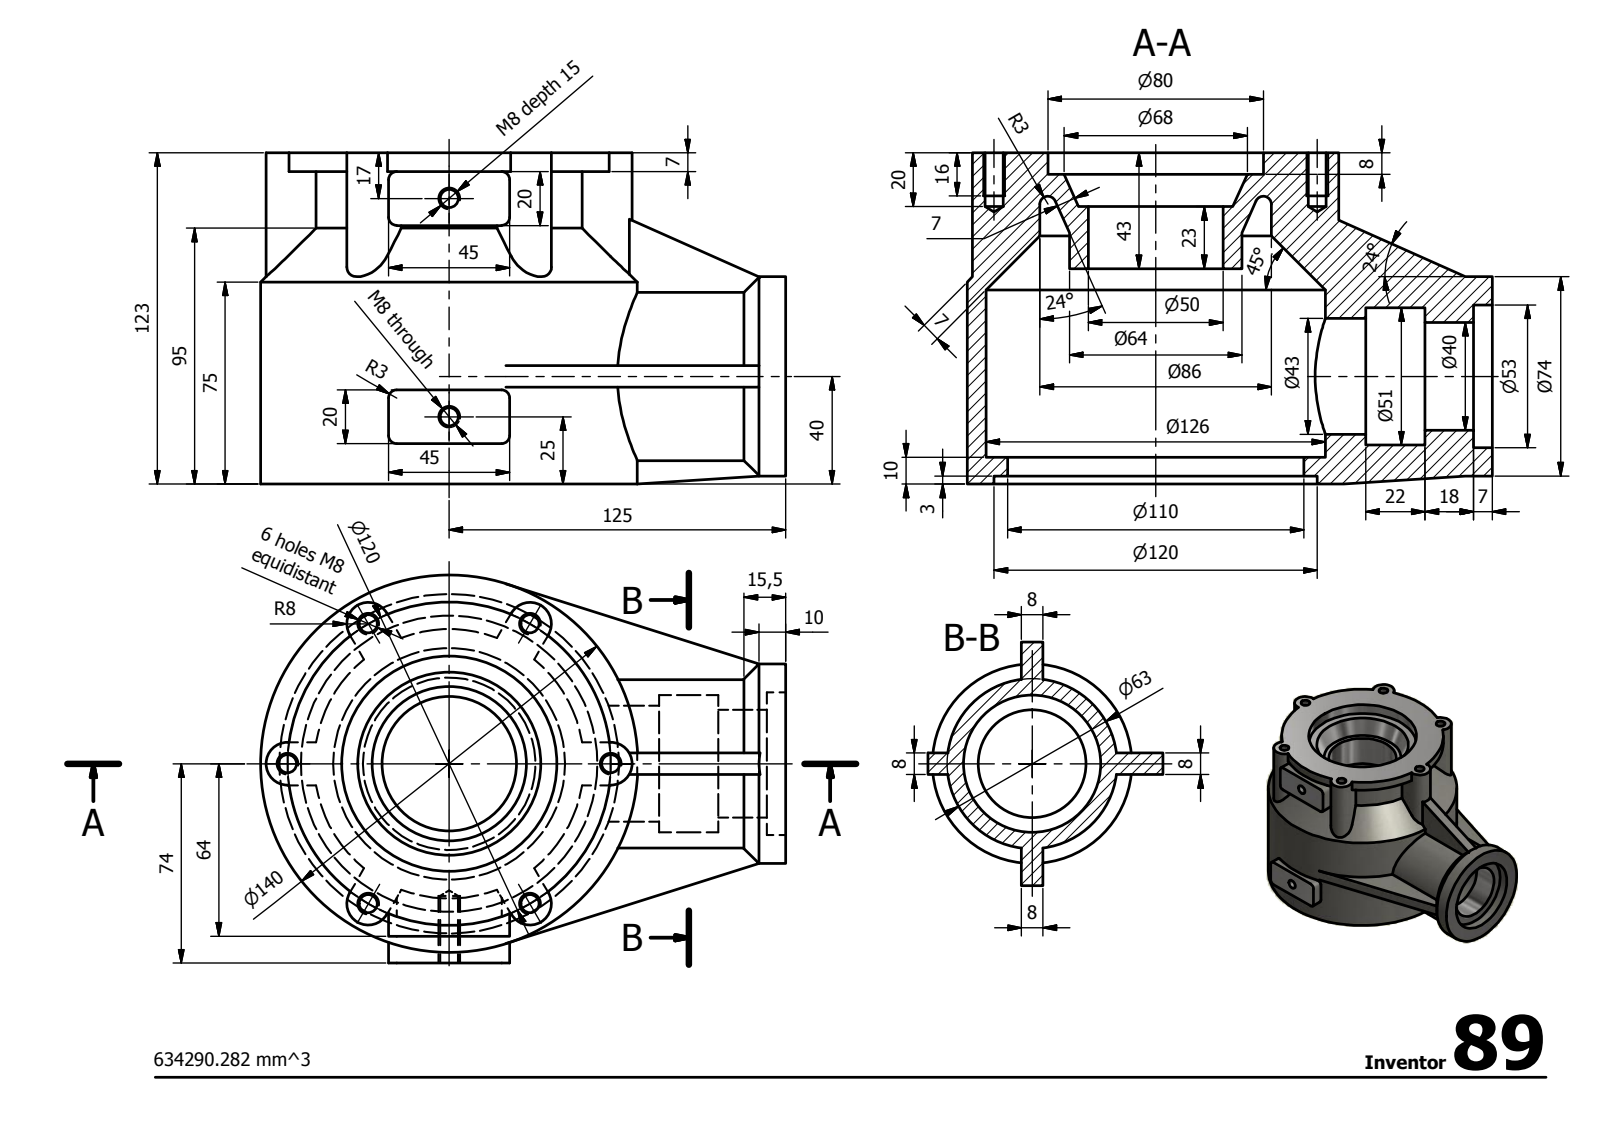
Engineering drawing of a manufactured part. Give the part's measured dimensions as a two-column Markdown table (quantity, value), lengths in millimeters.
| quantity | value |
| --- | --- |
| STEP written by | Autodesk Inventor 2014 (AUTOMOTIVE_DESIGN) |
| units | millimeters |
| bodies | 1 solid, 125 faces (58 planar, 51 cylindrical, 16 other) |
| overall size | 195 × 144 × 123 |
| volume | 634 289 mm³ |
| surface area | 167 668 mm² |
| round holes (diameter × count) | 6.65 × 8, 40 × 1, 43 × 1, 50 × 1, 51 × 1, 53 × 1, 80 × 1, 86 × 1, 110 × 1, 126 × 1 |
| round bosses / shafts (diameter × count) | 140 × 1, 120 × 1, 74 × 1, 64 × 1, 63 × 1 |
| partial cylindrical surfaces (radius × count) | 3 × 8, 8 × 6, 50 × 1 |
| main face-to-face distances | 7, 113, 36, 8, 123, 10, 80, 79, 44, 72 |
| hole center spacings | 60, 103.92, 120, 81 |
